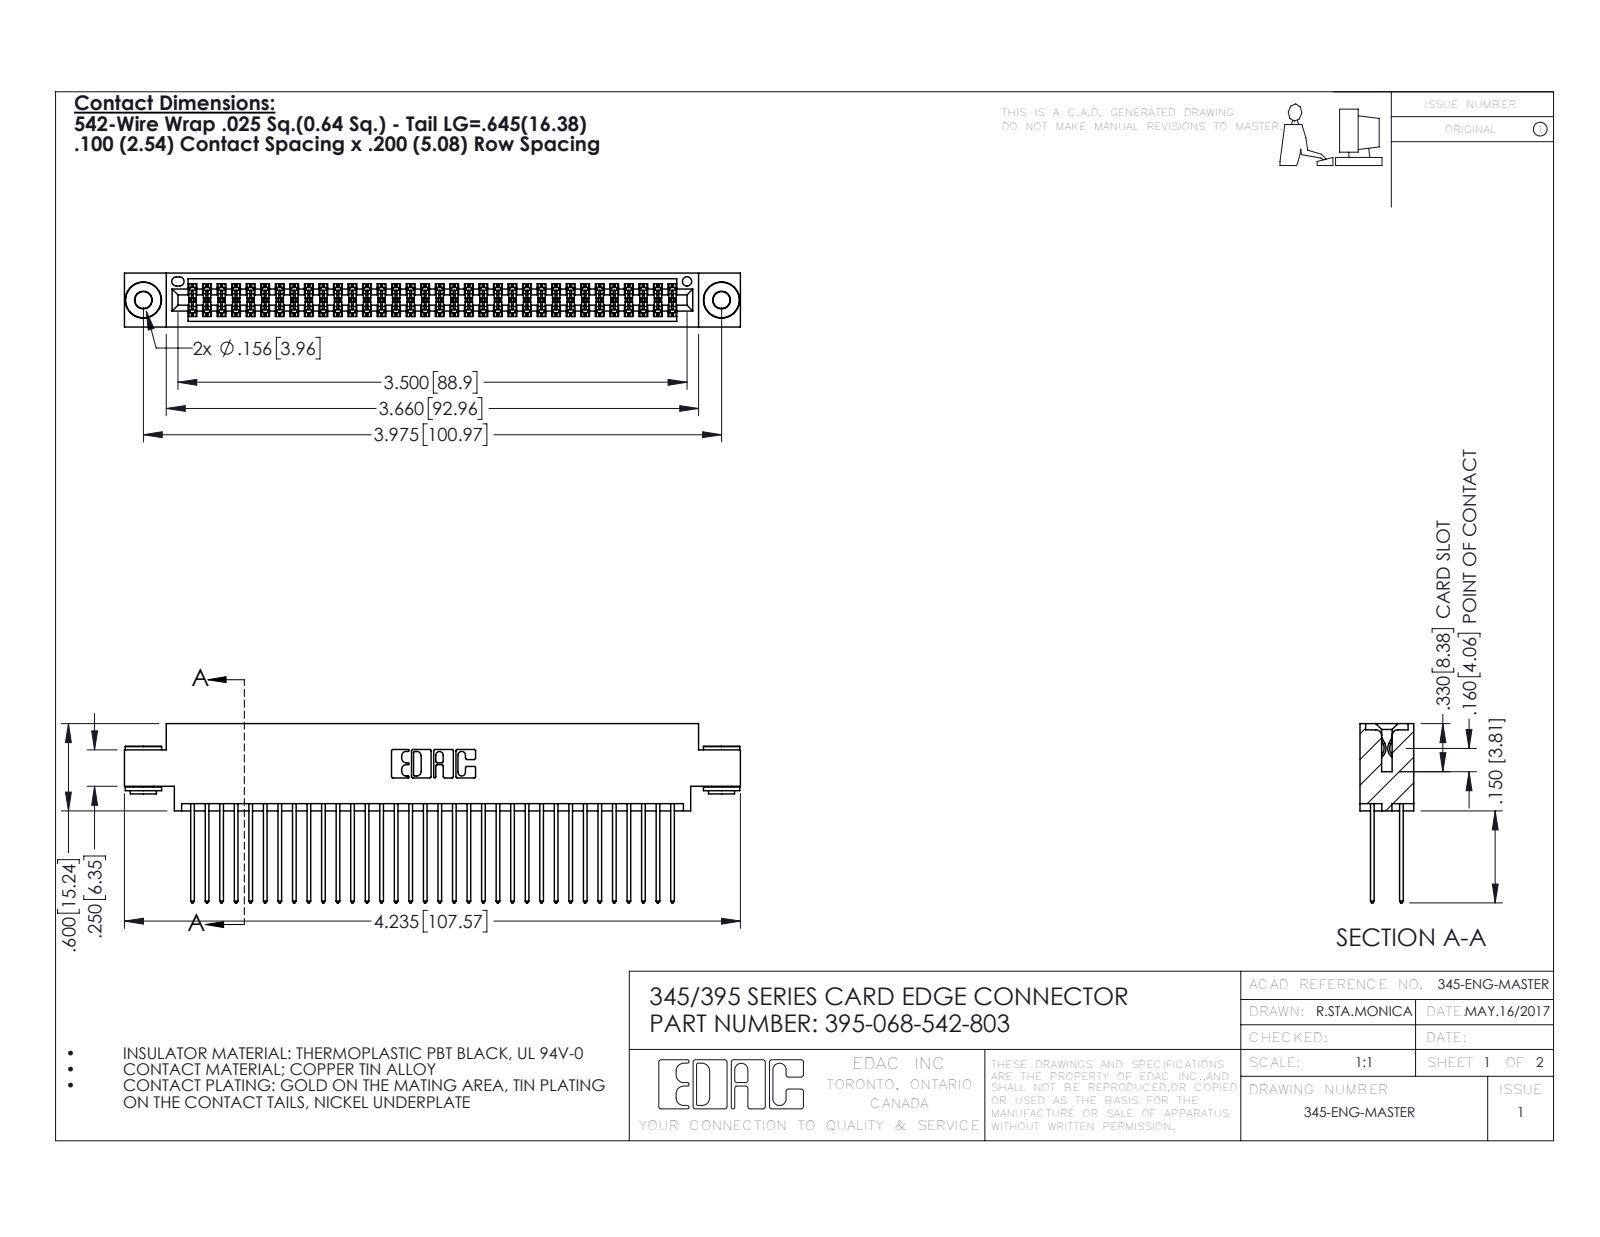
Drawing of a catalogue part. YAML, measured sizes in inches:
part_name: "345 Part_0.170 Offset - 0.156 Dia-TH; 395-068-542-803; 345-292-001_345-293-142; 345-250-002_345-250-002-102"
step_written_by: "SolidWorks 2016 (CONFIG_CONTROL_DESIGN)"
units: inches
bodies: {solids: 71, faces: 3568, planar: 2338, cylindrical: 1222, other: 8}
overall_size: [4.235, 1.232, 0.37]
volume: 0.647
surface_area: 26.88
round_holes:
  - {diameter: 0.116, count: 2}
  - {diameter: 0.156, count: 2}
  - {diameter: 0.064, count: 1}
round_bosses_or_shafts:
  - {diameter: 0.25, count: 2}
  - {diameter: 0.18, count: 2}
  - {diameter: 0.136, count: 2}
partial_cylinders:
  - {radius: 0.006, count: 102}
  - {radius: 0.01, count: 68}
  - {radius: 0.01, count: 22}
  - {radius: 0.007, count: 6}
  - {radius: 0.031, count: 6}
  - {radius: 0.026, count: 3}
  - {radius: 0.014, count: 2}
  - {radius: 0.019, count: 2}
face_to_face_distances: [0.072, 0.298, 0.2, 0.098, 0.272, 0.025, 0.37, 0.225, 0.175, 0.149]
hole_center_spacings: [0.27, 3.74, 3.975]
